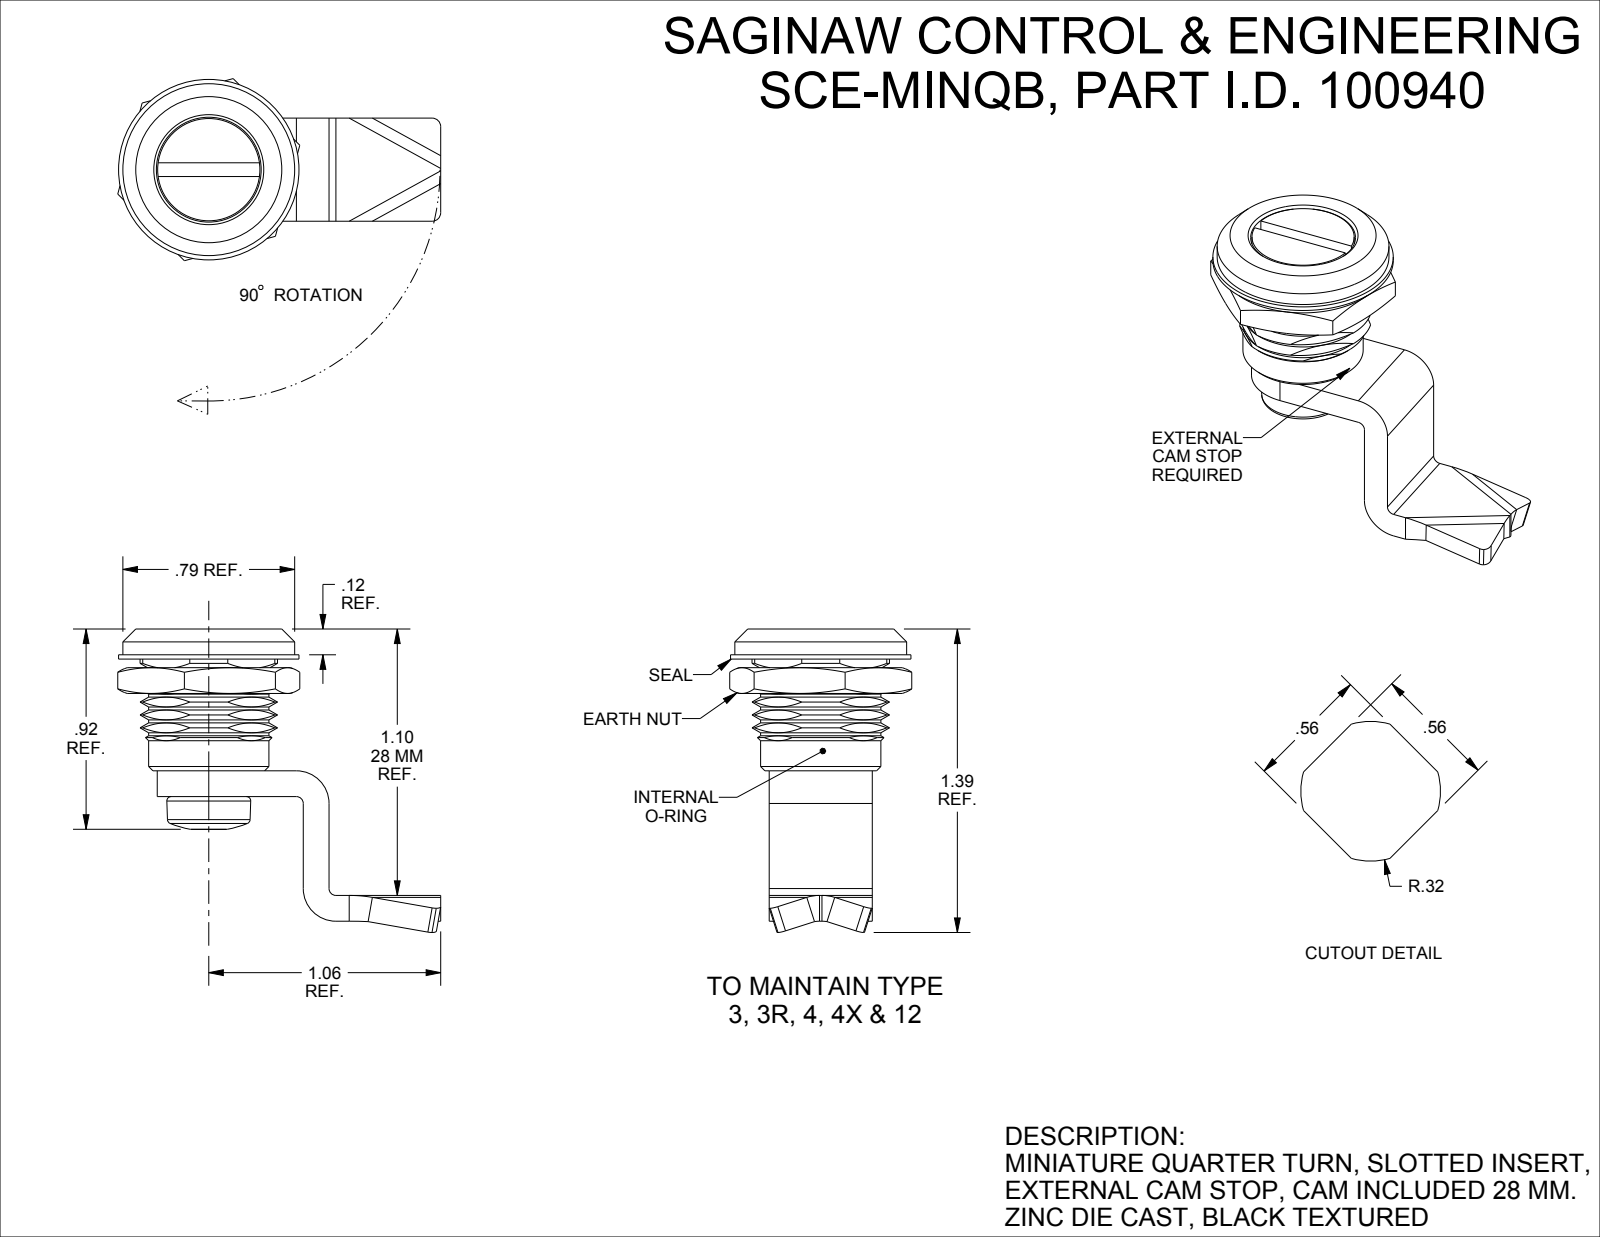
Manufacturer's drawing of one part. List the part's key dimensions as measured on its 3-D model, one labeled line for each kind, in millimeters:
Part name (STEP PRODUCT): SCE-MINQB
STEP written by: SolidWorks 2019 (CONFIG_CONTROL_DESIGN)
Units: millimetres
Bodies: 8 solids, 418 faces (124 planar, 91 cylindrical, 203 other)
Overall size (bounding box): 35.3 × 33.9 × 33.4
Volume: 4 970 mm³ · Surface area: 6 195 mm²
Round holes (diameter × count): ⌀4.1 ×1, ⌀8 ×1, ⌀8.3 ×1, ⌀12.2 ×1, ⌀14.9 ×1
Round bosses / shafts (diameter × count): ⌀21 ×1, ⌀20 ×1, ⌀14 ×1, ⌀11.9 ×1, ⌀11.5 ×1, ⌀7.9 ×1
Partial cylindrical surfaces — rounded edges, fillets, slot ends (radius × count): R0.3 ×12, R1 ×6, R0.8 ×4, R3.8 ×4, R0.5 ×3, R4.6 ×1, R4.9 ×1, R6 ×1
Main face-to-face distances: 3, 16.5, 12, 13.5, 0.5, 13, 14.5, 31, 16, 4.5
